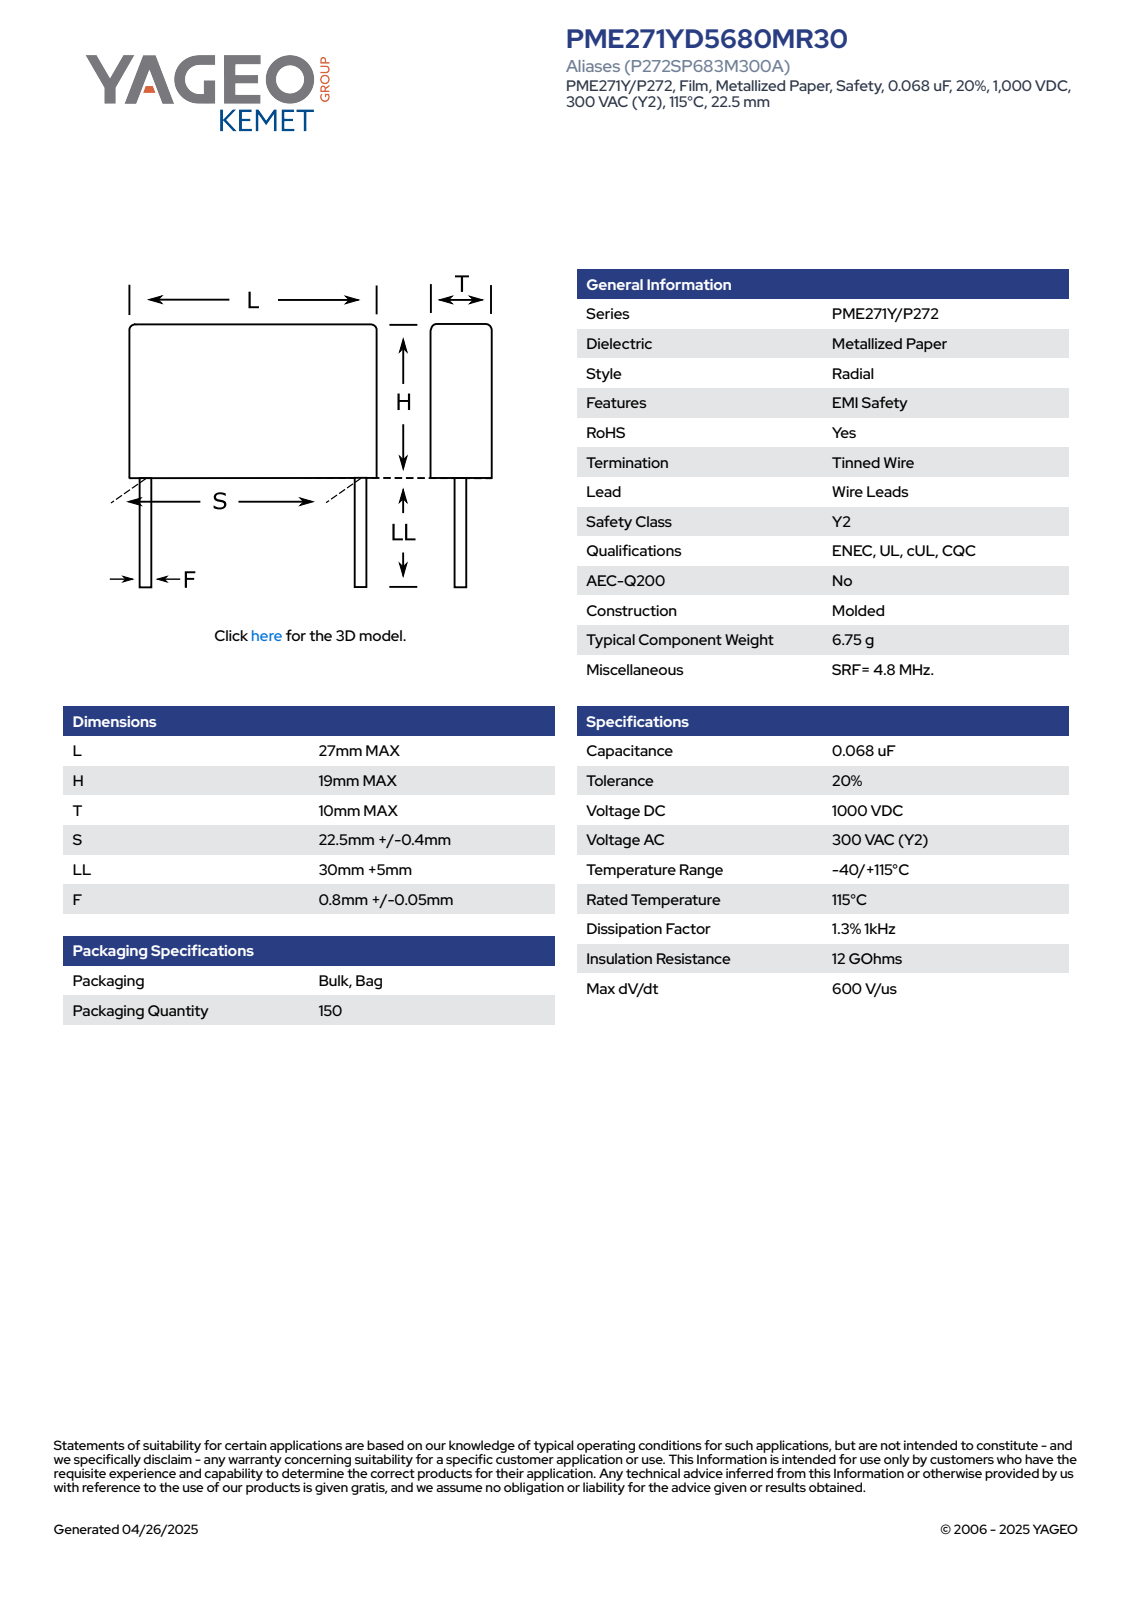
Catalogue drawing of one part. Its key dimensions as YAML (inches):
part_name: "CFR_MOLDED_27X19X10_L27H19T10S22.5LL35F0.85"
step_written_by: "SolidWorks 2014 (AUTOMOTIVE_DESIGN)"
units: inches
bodies: {solids: 4, faces: 73, planar: 65, cylindrical: 8, other: 0}
overall_size: [2.126, 1.063, 0.394]
volume: 0.315
surface_area: 3.336
round_bosses_or_shafts:
  - {diameter: 0.033, count: 2}
partial_cylinders:
  - {radius: 0.02, count: 4}
face_to_face_distances: [0.394, 0.748, 1.063, 0.394, 1.378, 2.126, 1.787, 0.409, 0.339, 1.692]
